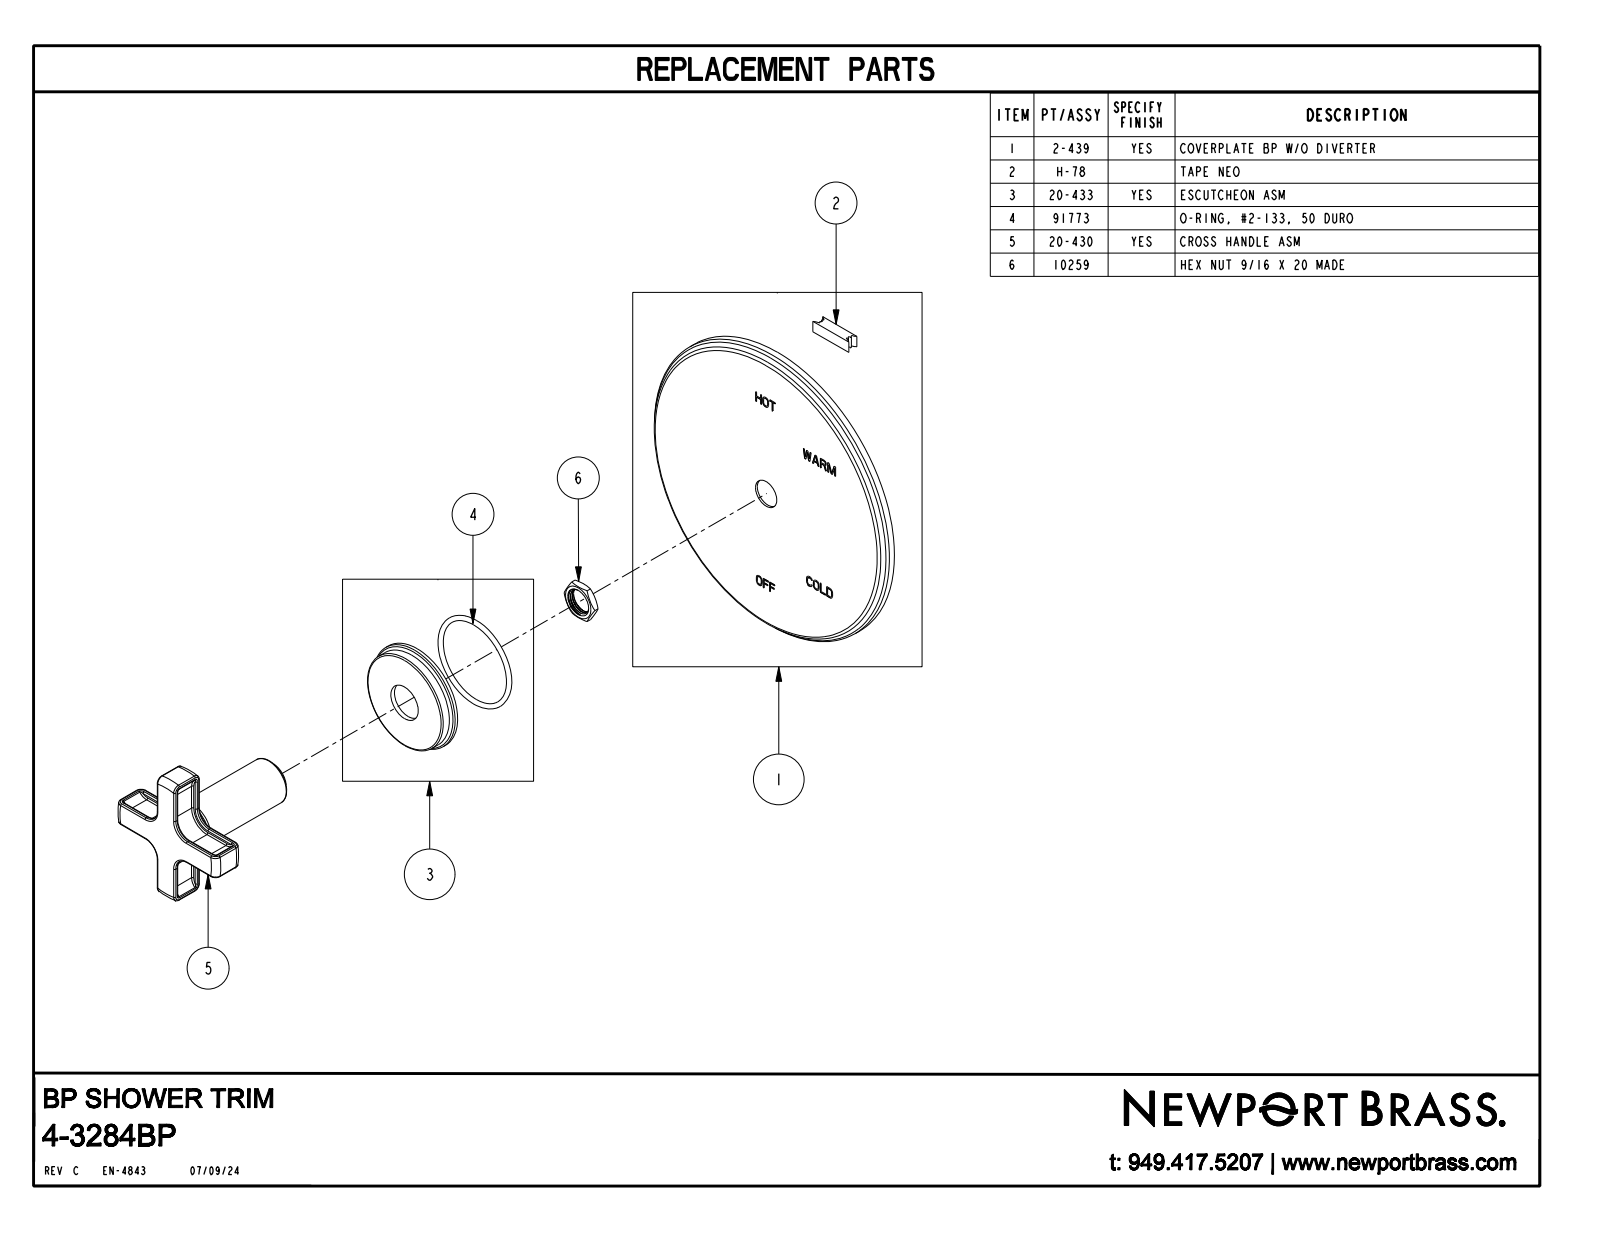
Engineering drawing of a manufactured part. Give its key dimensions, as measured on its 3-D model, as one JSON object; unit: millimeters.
{"part_name": "11117; H-78; 2-439_ASM; 13130 (+8 more)", "step_written_by": "CREO PARAMETRIC BY PTC INC, 2018400 (CONFIG_CONTROL_DESIGN)", "units": "millimeters", "bodies": {"solids": 12, "faces": 1313, "planar": 546, "cylindrical": 451, "other": 316}, "overall_size": [165.1, 165.1, 90.5], "volume_mm3": 87100, "surface_area_mm2": 120400, "round_holes": [[2.8, 1], [4.3, 1], [7, 1], [9.1, 1], [9.1, 1], [9.5, 1], [9.7, 1], [10.1, 1], [10.2, 1], [13.1, 1], [15, 1], [15.2, 1]], "round_bosses_or_shafts": [[165.1, 1], [57.2, 1], [53.1, 1], [46, 1], [24.8, 1], [21.6, 1], [18.5, 1], [13, 1]], "partial_cylinders_radius": [[0.8, 40], [6.4, 8], [0.3, 6], [1.1, 6], [8.3, 4], [10.8, 4], [1.8, 1], [3.5, 1]], "face_to_face_distances": [1.3, 10.2, 8.9, 73.7, 83.8, 82.6, 2.5, 64.8, 17.8, 66.1]}
